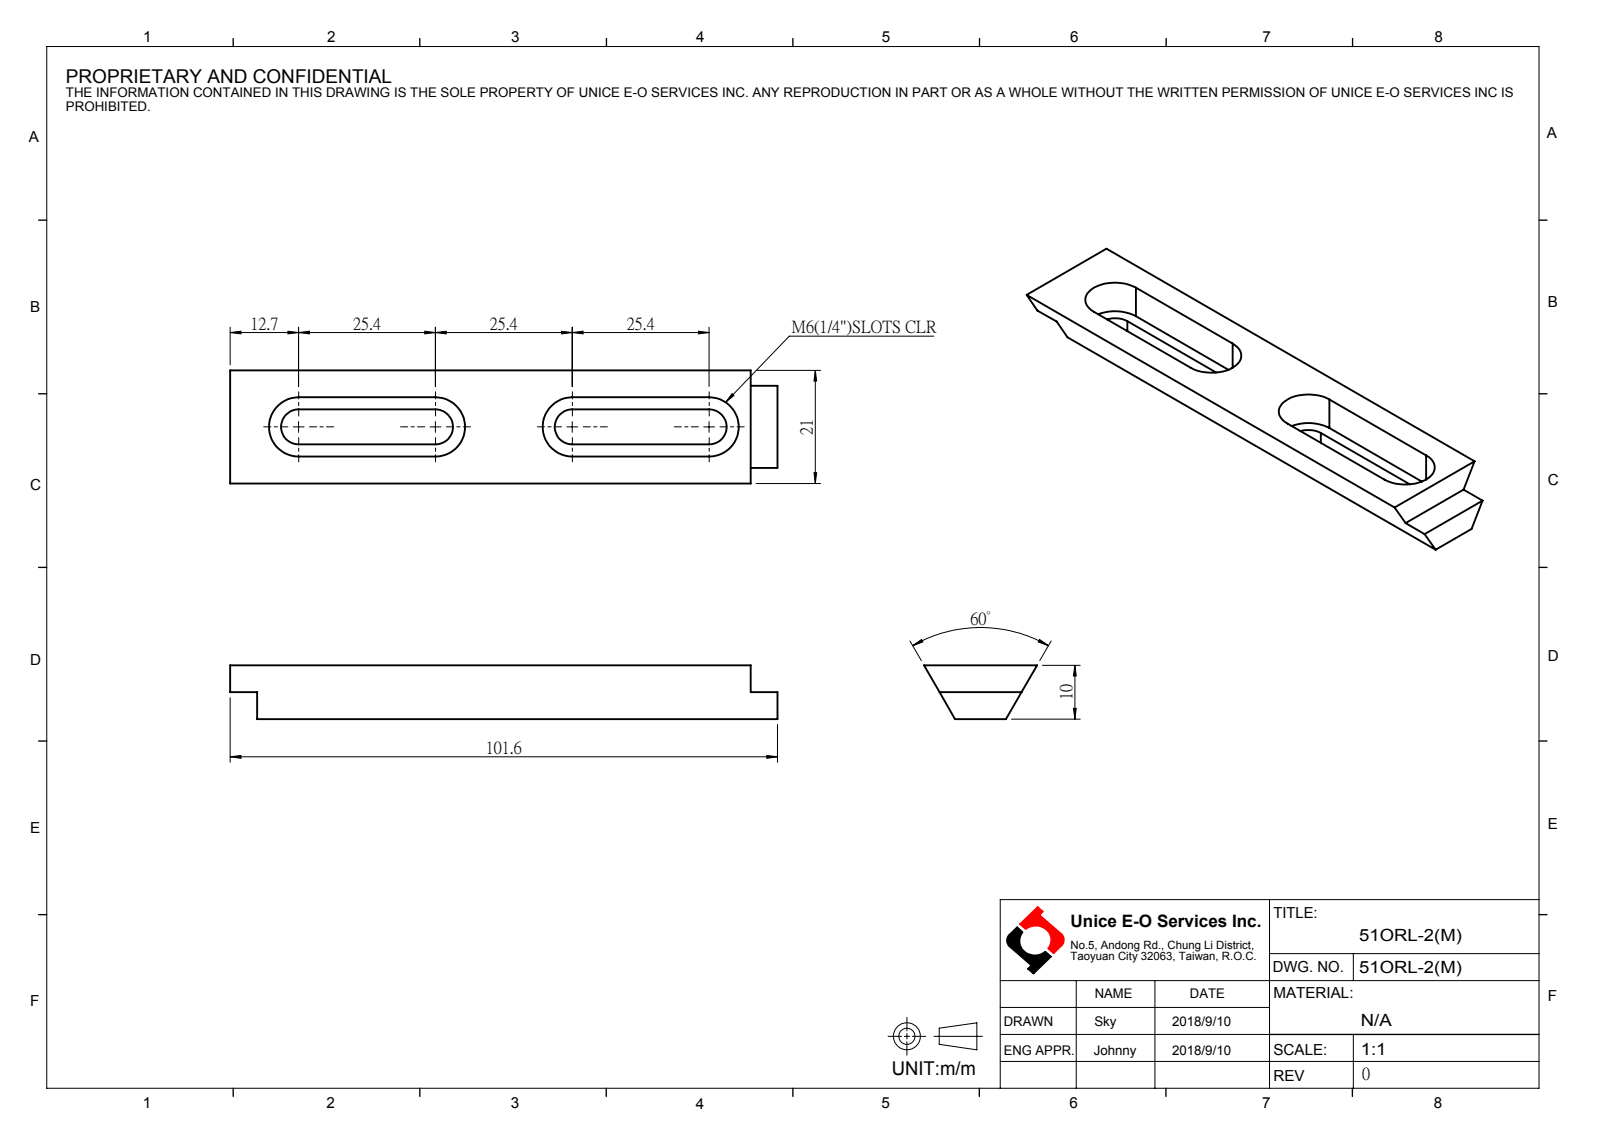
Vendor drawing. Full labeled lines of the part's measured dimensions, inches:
Part name (STEP PRODUCT): 51ORL-2(M)
STEP written by: SolidWorks 2016 (AUTOMOTIVE_DESIGN)
Units: inches
Bodies: 0 solids, 28 faces (20 planar, 8 cylindrical, 0 other)
Overall size (bounding box): 4 × 0.827 × 0.394
Partial cylindrical surfaces — rounded edges, fillets, slot ends (radius × count): R0.128 ×4, R0.217 ×4
Main face-to-face distances: 0.256, 0.394, 0.197, 0.089, 0.344, 0.138, 0.433, 3.803, 0.059, 4
